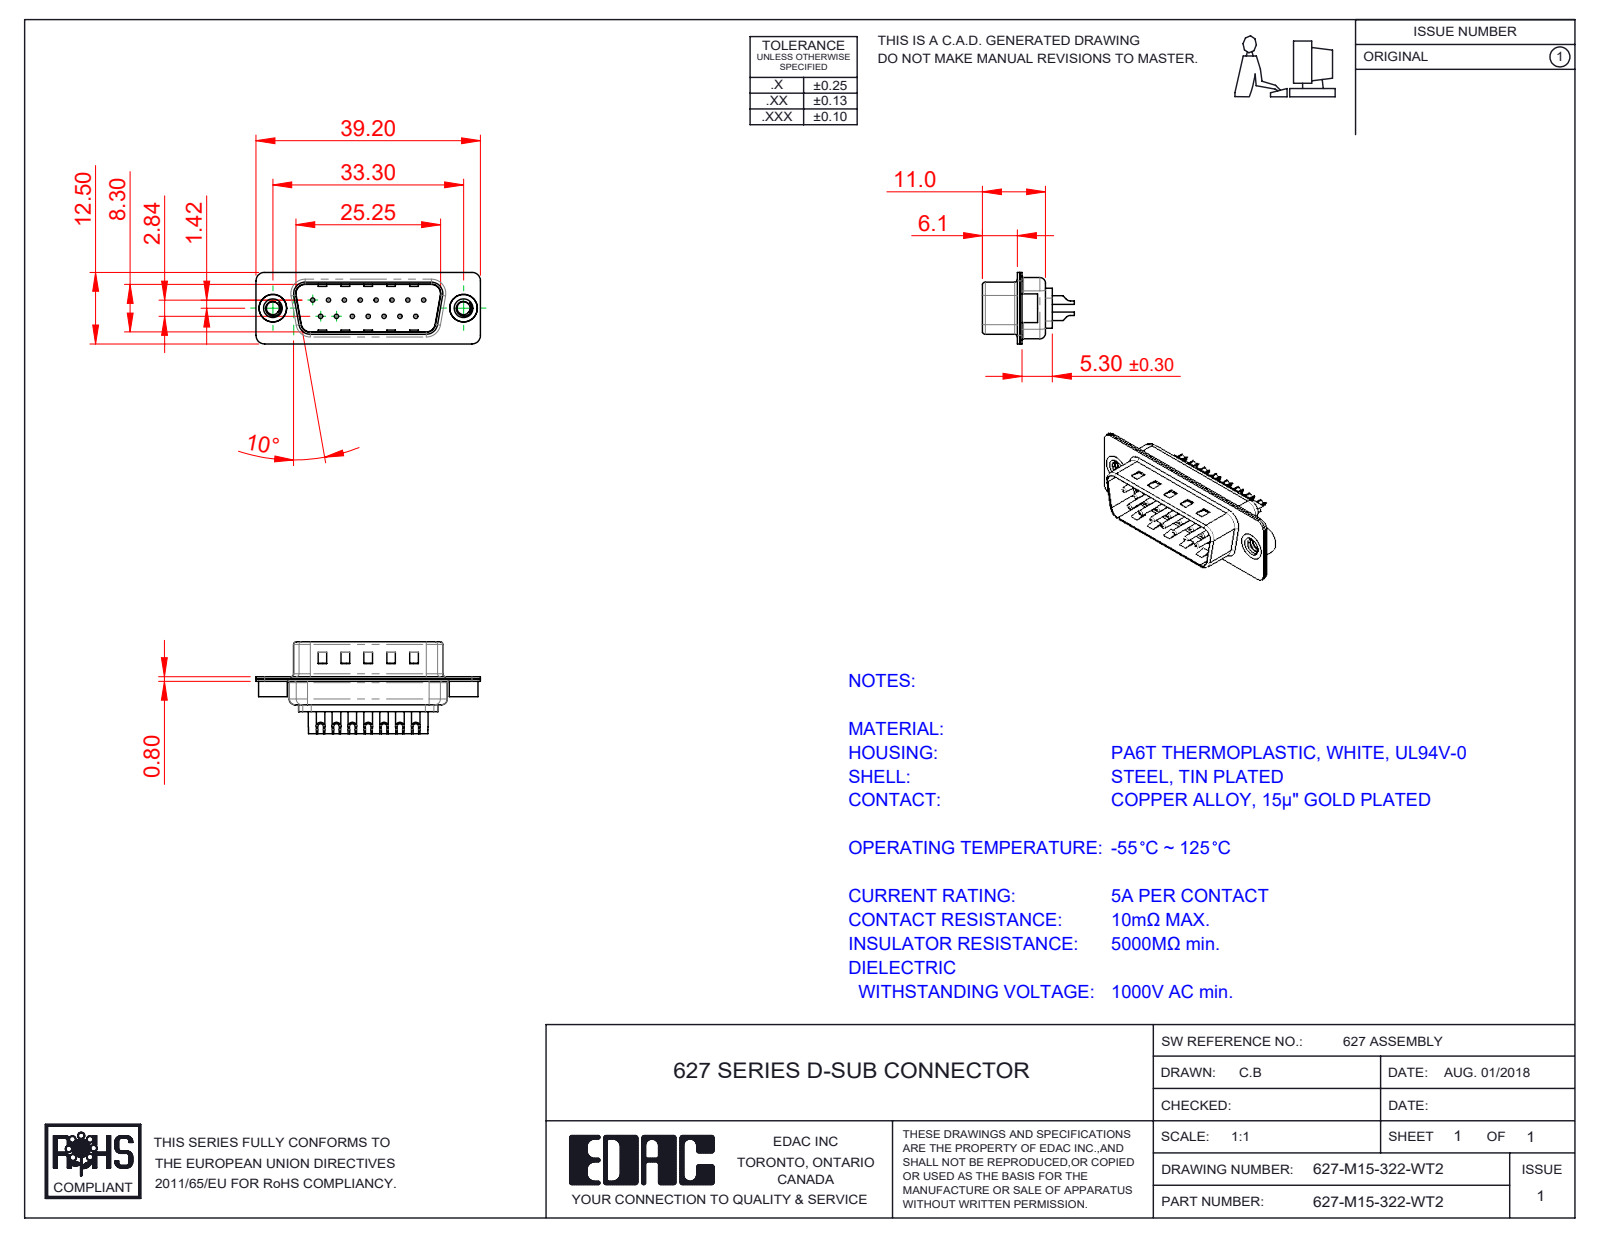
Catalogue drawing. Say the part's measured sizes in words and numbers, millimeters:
The part is named "627M Housing_15 Contacts; 627M Contact Row 1_22; 627M Shell Front_15 Contacts; 627-M15-322-WT2 (+3 more)". Its 3-D file was written by "SolidWorks 2020 (CONFIG_CONTROL_DESIGN)". It is 20 solids with 895 faces: 274 planar, 373 cylindrical and 248 other. Overall it measures 39.2 by 16.05 by 12.5 millimeters. Its volume is 1 878 cubic millimeters and its surface area 4 949 square millimeters. Round holes: 15 of diameter 0.75, 15 of diameter 1, 15 of diameter 1.6, 15 of diameter 2, 2 of diameter 2.26, 2 of diameter 4, 2 of diameter 4.8. Round bosses or shafts: 15 of diameter 1.5, 2 of diameter 5, 2 of diameter 4.9. Partial cylindrical surfaces (rounded edges, fillets, slot ends): 16 of radius 1.5, 12 of radius 2, 8 of radius 0.5, 8 of radius 1.6, 6 of radius 1, 4 of radius 0.25, 4 of radius 0.6, 4 of radius 0.65. The main face-to-face distances are 0.4, 0.8, 9.5, 9.1, 8.7, 9.9, 1.2, 0.75, 0.35, 6.1. The hole center spacings are 3.16, 2.77, 5.54, 8.31, 11.08, 5.03, 5.04, 7.48.
